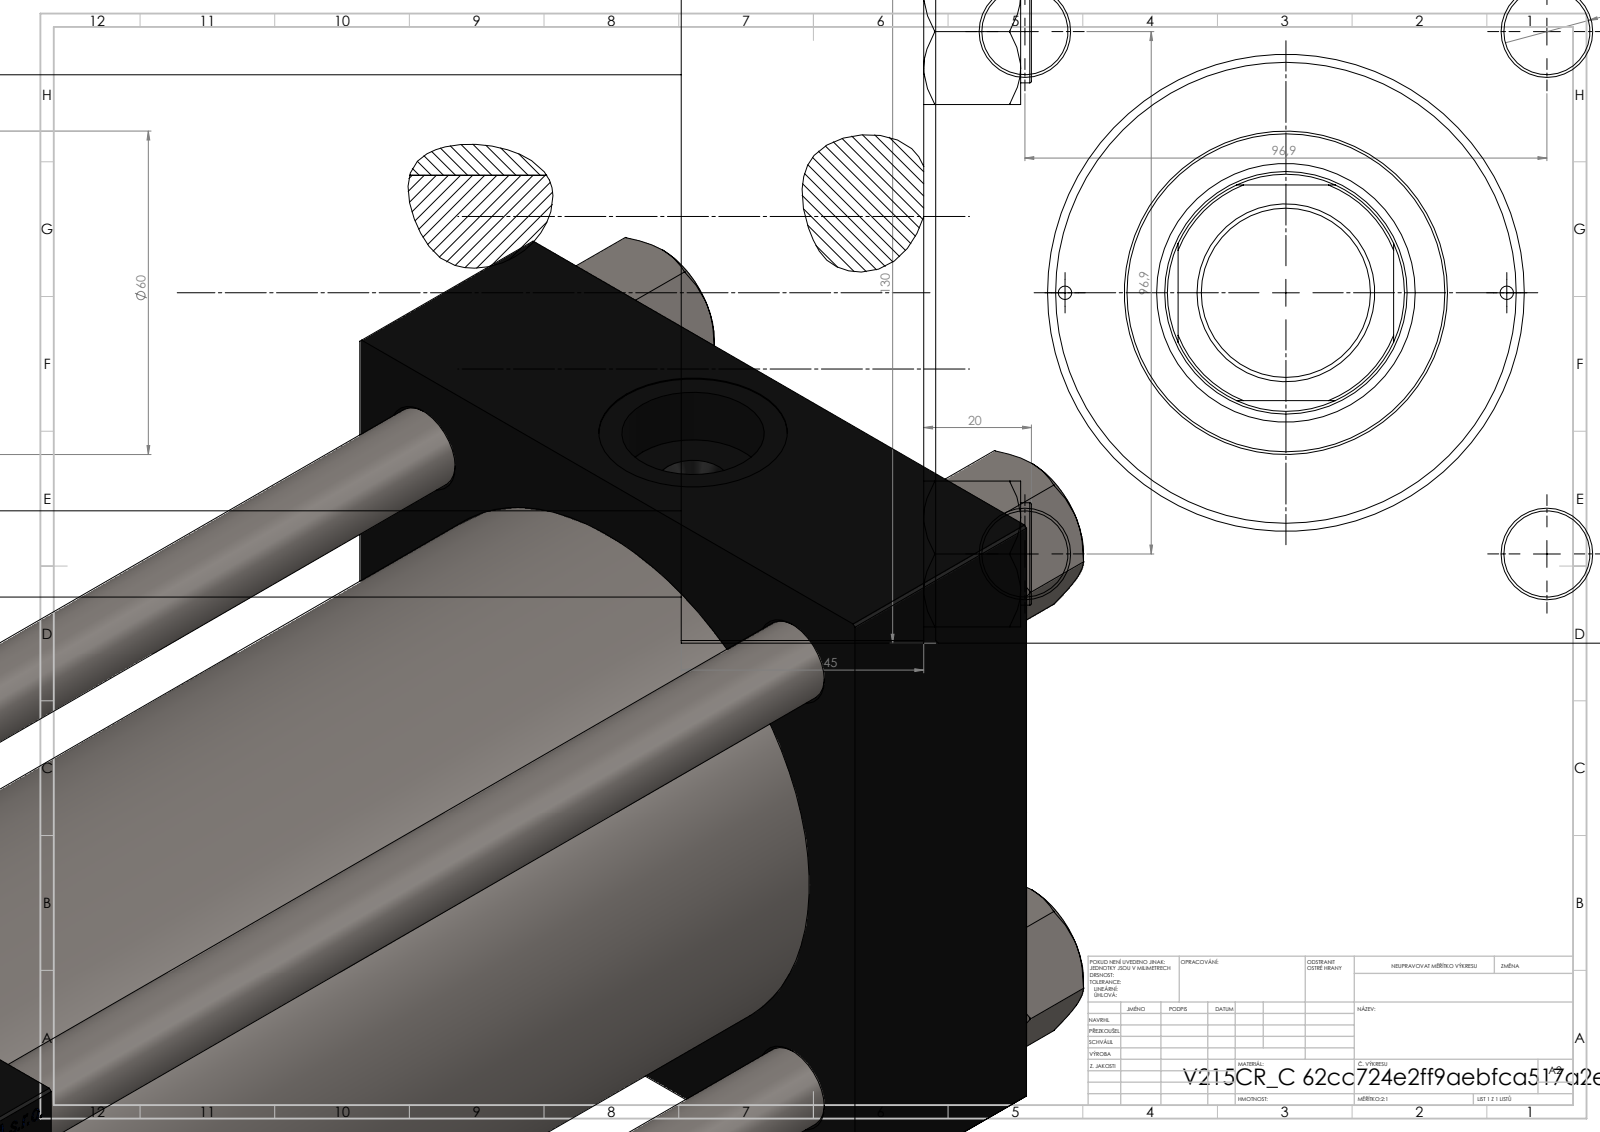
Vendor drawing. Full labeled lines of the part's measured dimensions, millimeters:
Part name (STEP PRODUCT): V215CR_C_Body; V215CR_VCP_C; ROD_END_AH; V215CR_C_TYCINKA (+2 more)
STEP written by: SolidWorks 2019 (CONFIG_CONTROL_DESIGN)
Units: millimetres
Bodies: 12 solids, 1217 faces (580 planar, 95 cylindrical, 542 other)
Overall size (bounding box): 428 × 130 × 130
Volume: 2 934 000 mm³ · Surface area: 471 483 mm²
Round holes (diameter × count): ⌀16 ×4, ⌀2.5 ×2, ⌀7 ×2, ⌀26.44 ×2, ⌀35 ×2, ⌀31.5 ×1, ⌀45 ×1, ⌀48 ×1, ⌀76 ×1, ⌀85.5 ×1, ⌀100 ×1
Round bosses / shafts (diameter × count): ⌀19 ×4, ⌀106 ×1, ⌀60 ×1, ⌀33 ×1, ⌀31 ×1
Partial cylindrical surfaces — rounded edges, fillets, slot ends (radius × count): R22 ×1
Main face-to-face distances: 130, 45, 328, 283, 256, 211, 72, 96, 51, 160
Hole centre spacings: 49.02, 68.52, 96.9, 101.73, 41, 137.04, 82, 258.5
